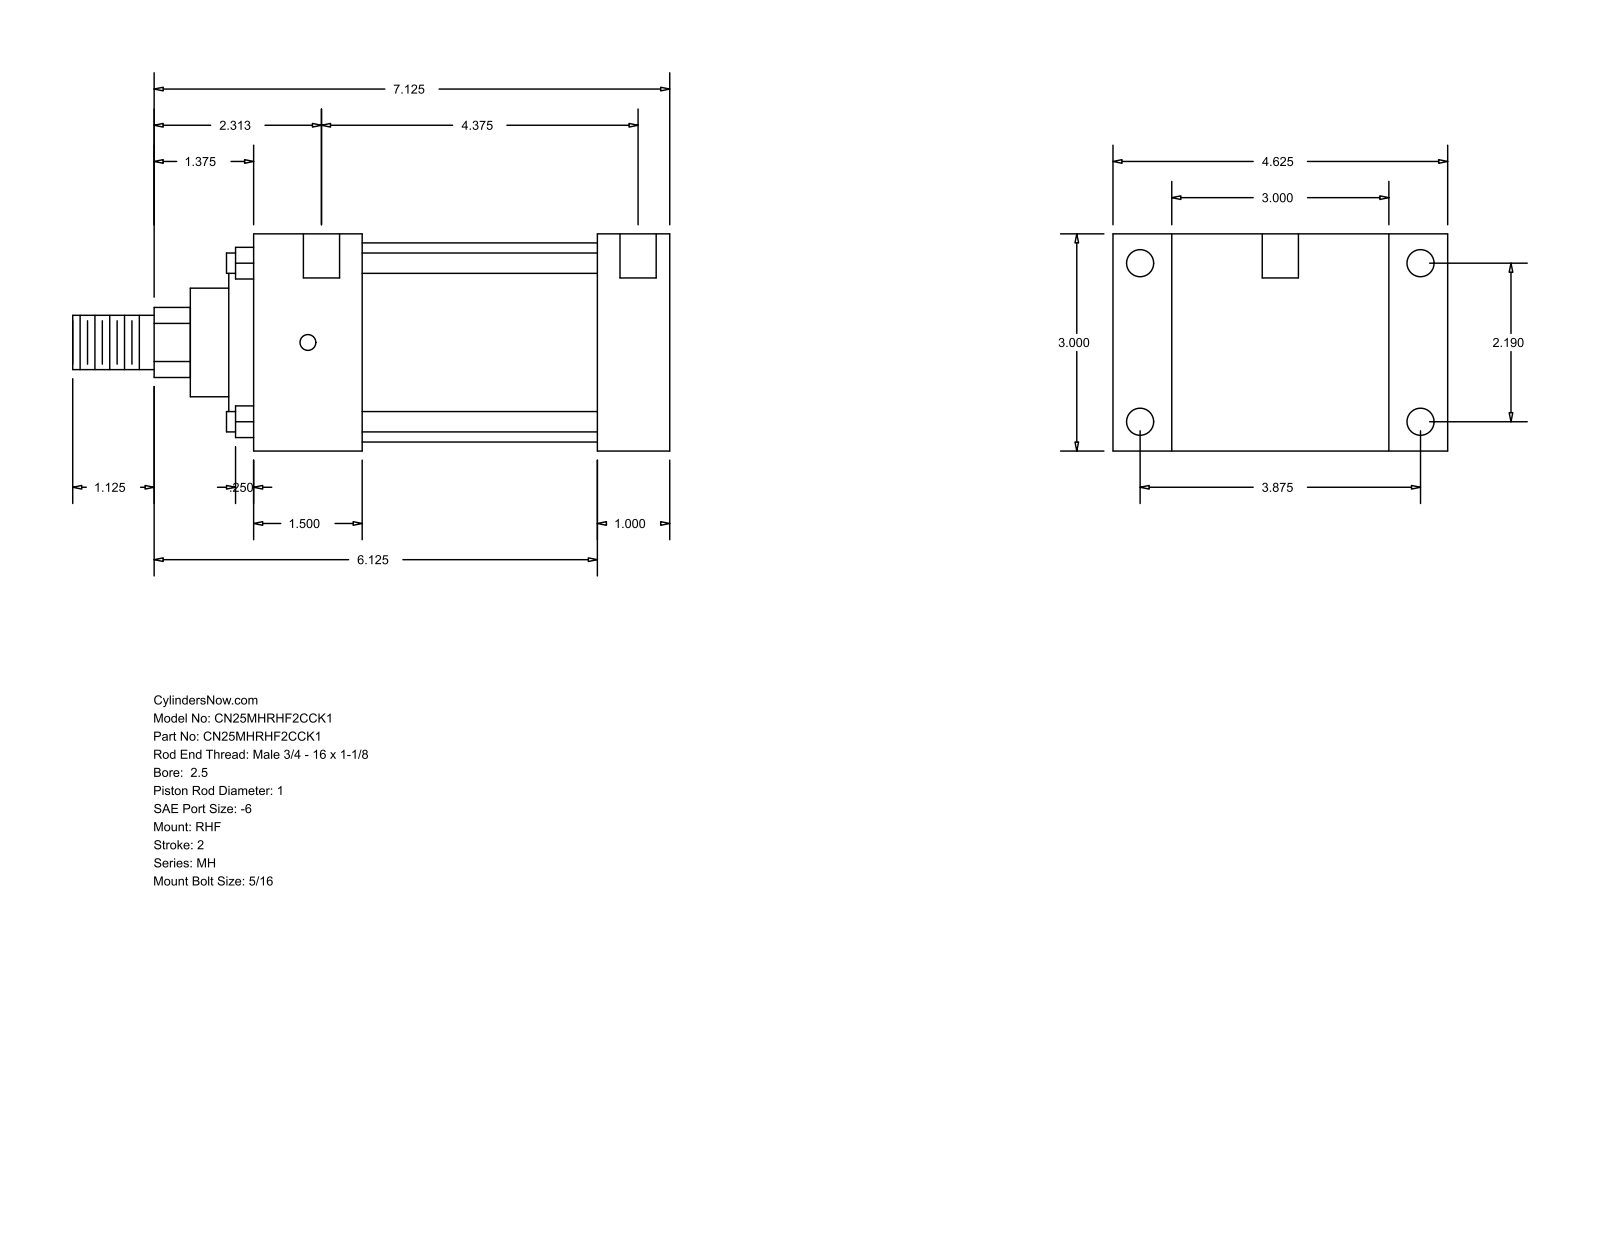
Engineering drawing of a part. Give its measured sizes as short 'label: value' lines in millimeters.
name: MH_RHF__0250_1
written by: GSSL Pune (CONFIG_CONTROL_DESIGN)
unit: mm
bodies: 0 solids, 90 faces (61 planar, 29 cylindrical, 0 other)
size: 209.55 × 117.47 × 76.2
holes: 4× ⌀5.56, 4× ⌀9.53, 2× ⌀12.7
bosses: 4× ⌀7.14, 1× ⌀69.85, 1× ⌀60.33, 1× ⌀38.1, 1× ⌀25.4, 1× ⌀19.05
rounds: 1× R12.29
face distances: 76.2, 25.4, 20.64, 96.84, 120.65, 146.05, 117.48, 38.11, 82.54, 107.94
hole spacings: 55.62, 98.42, 113.05, 119.06, 3.18, 4.76, 111.12, 114.3
